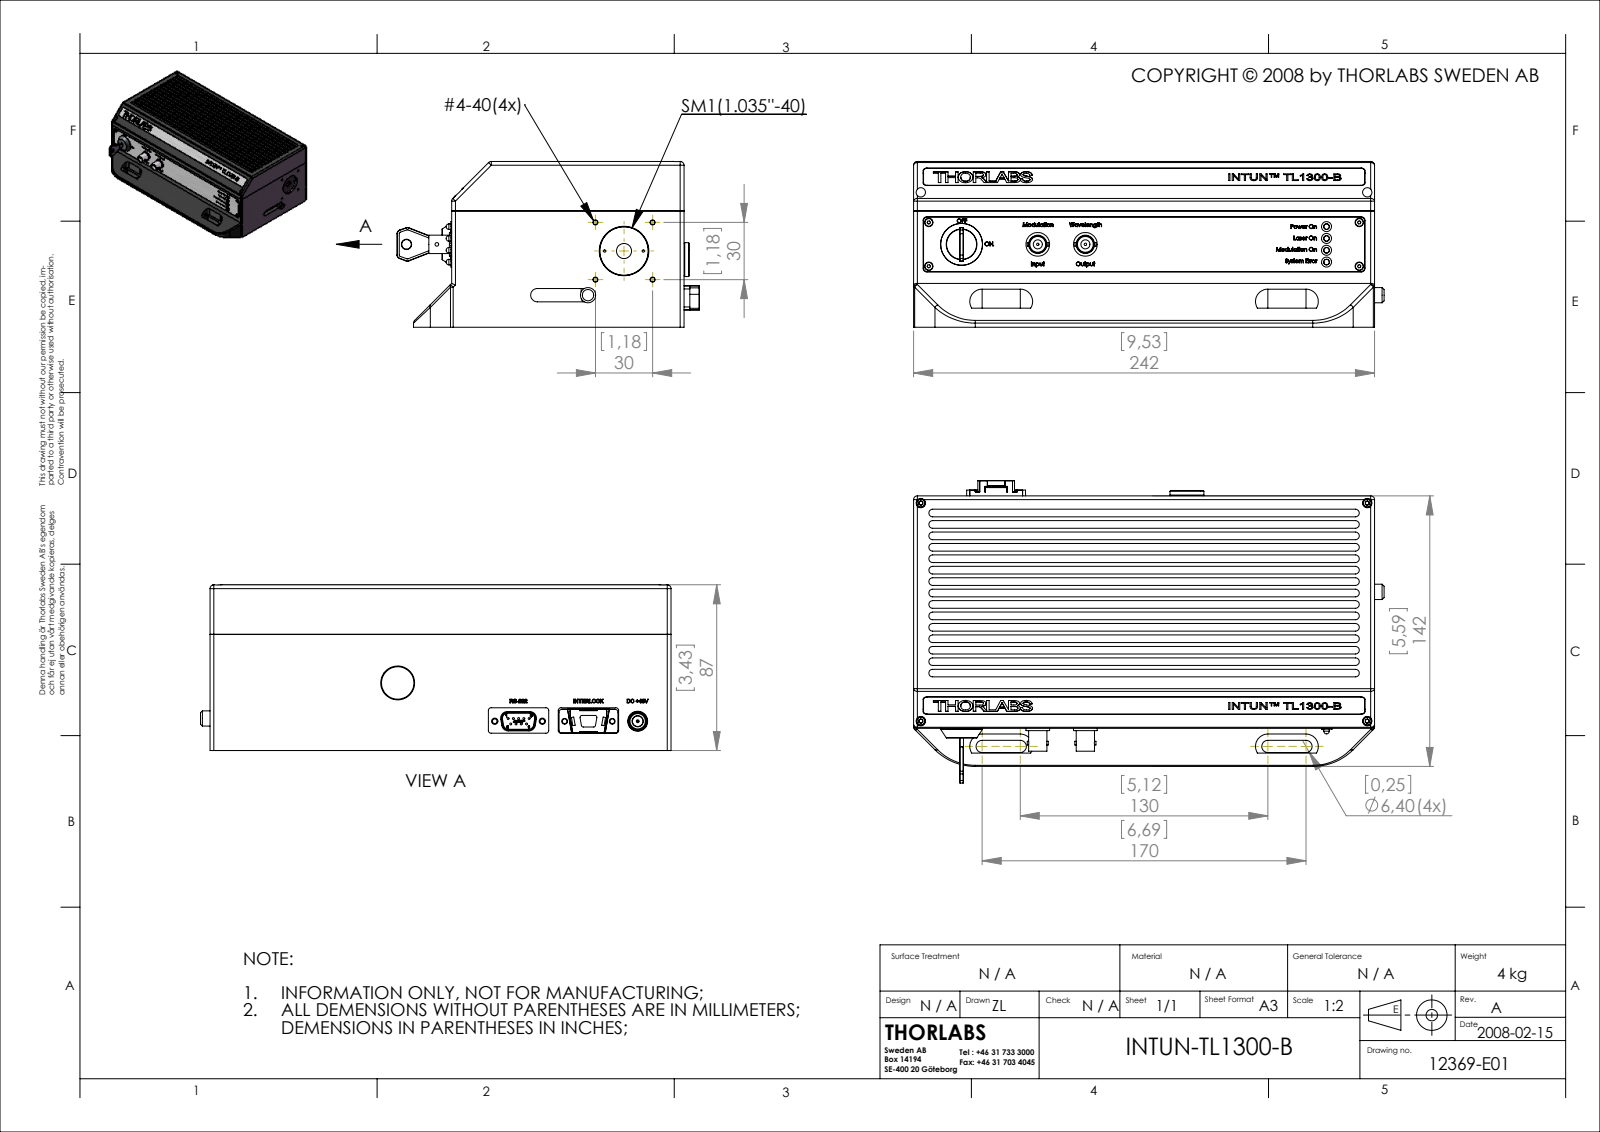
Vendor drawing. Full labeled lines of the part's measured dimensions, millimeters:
Part name (STEP PRODUCT): INTUN-TL1300-B
STEP written by: SolidWorks 2007 (CONFIG_CONTROL_DESIGN)
Units: millimetres
Bodies: 0 solids, 3235 faces (1793 planar, 636 cylindrical, 806 other)
Overall size (bounding box): 247 × 158.68 × 87
Round holes (diameter × count): ⌀1.02 ×9, ⌀2.05 ×8, ⌀1.6 ×4, ⌀2.26 ×4, ⌀2.4 ×4, ⌀2.5 ×4, ⌀2.9 ×4, ⌀3 ×4, ⌀3.05 ×4, ⌀4.3 ×4, ⌀4.5 ×4, ⌀4.9 ×4
Round bosses / shafts (diameter × count): ⌀1.02 ×9, ⌀4.5 ×5, ⌀2.5 ×5, ⌀6.2 ×4, ⌀5.3 ×4, ⌀4.7 ×4, ⌀4.25 ×4, ⌀4 ×4
Partial cylindrical surfaces — rounded edges, fillets, slot ends (radius × count): R2 ×68, R1.57 ×16, R0.2 ×14, R5 ×14, R3.5 ×10, R6 ×10, R0.71 ×9, R0.94 ×9
Main face-to-face distances: 6, 5.6, 6.25, 77.75, 72.15, 116, 2, 1, 83, 5.25
Hole centre spacings: 2.77, 23, 15.76, 21.21, 29.29, 30, 3.15, 5.02
